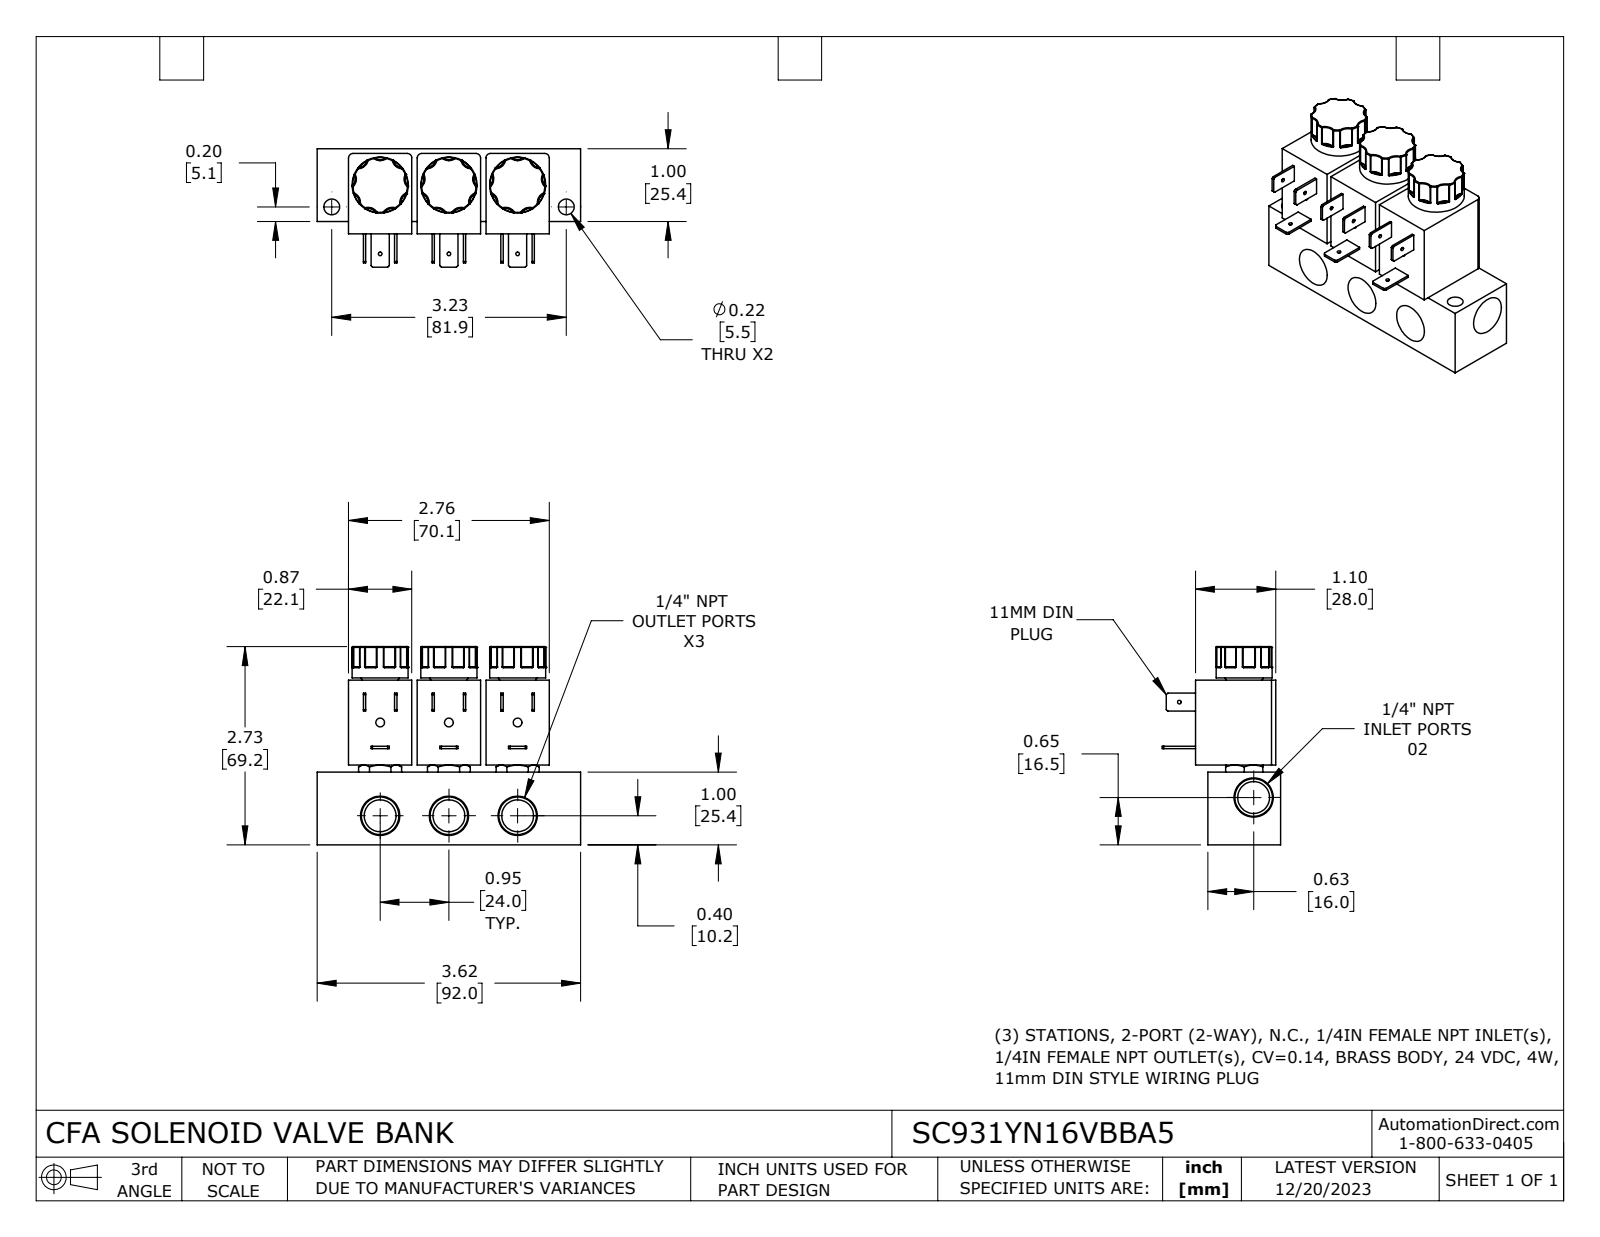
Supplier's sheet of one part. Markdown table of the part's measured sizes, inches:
| quantity | value |
| --- | --- |
| part name | SC931YN16VBBA5 |
| STEP written by | SolidWorks 2023 (CONFIG_CONTROL_DESIGN) |
| units | inches |
| bodies | 1 solid, 657 faces (146 planar, 140 cylindrical, 371 other) |
| overall size | 3.622 × 2.725 × 1.627 |
| volume | 7.008 in³ |
| surface area | 47.81 in² |
| round holes (diameter × count) | 0.05 × 4, 0.438 × 4, 0.12 × 3, 0.217 × 2 |
| round bosses / shafts (diameter × count) | 0.77 × 3 |
| partial cylindrical surfaces (radius × count) | 0.01 × 54, 0.133 × 25, 0.06 × 6, 0.132 × 2 |
| main face-to-face distances | 1, 0.945, 0.87, 1.169, 0.169, 0.065, 0.935, 1.104, 1.89, 1.815 |
| hole center spacings | 0.945, 1.593, 1.282, 1.89, 2.283, 0.928, 0.93, 1.662 |
